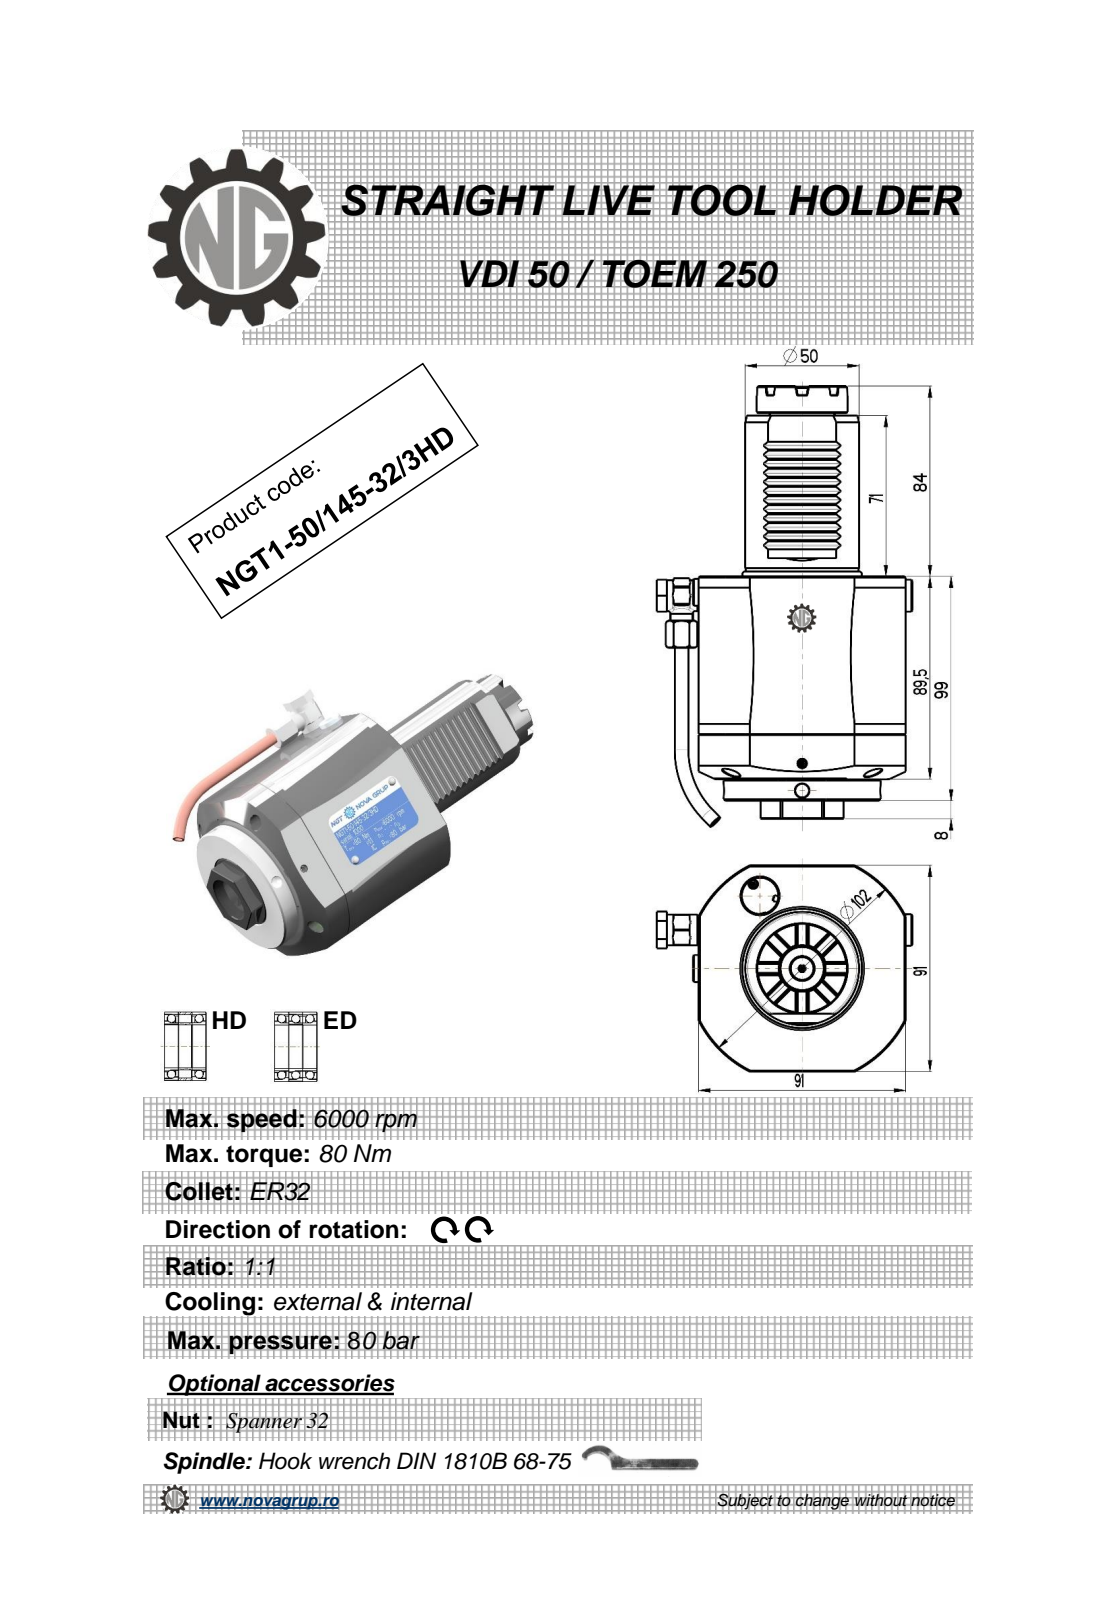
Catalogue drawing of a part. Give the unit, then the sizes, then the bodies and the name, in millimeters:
Units: millimetres
Overall size (bounding box): 194.44 × 112.4 × 91
Round holes (diameter × count): ⌀4 ×3, ⌀6 ×2, ⌀3 ×1, ⌀6.2 ×1, ⌀9 ×1, ⌀10 ×1, ⌀11 ×1, ⌀23 ×1, ⌀34 ×1
Round bosses / shafts (diameter × count): ⌀6 ×2, ⌀69 ×1, ⌀50 ×1, ⌀40 ×1, ⌀20.5 ×1, ⌀14 ×1, ⌀13.6 ×1, ⌀13 ×1
Partial cylindrical surfaces — rounded edges, fillets, slot ends (radius × count): R0.3 ×12, R0.41 ×6, R0.5 ×4, R6.25 ×1, R7.7 ×1, R51 ×1
Main face-to-face distances: 91, 99, 9.5, 89.5, 2.83, 170, 160.5, 71, 14.14, 11.31
Hole centre spacings: 0.4, 55.66, 56.04, 87.66
Volume: 841 247 mm³ · Surface area: 68 112 mm²
Bodies: 1 solid, 433 faces (185 planar, 96 cylindrical, 152 other)
Part name (STEP PRODUCT): NGT1_50_145_32_3HD
STEP written by: PRO/ENGINEER BY PARAMETRIC TECHNOLOGY CORPORATION, 2010280 (CONFIG_CONTROL_DESIGN)
